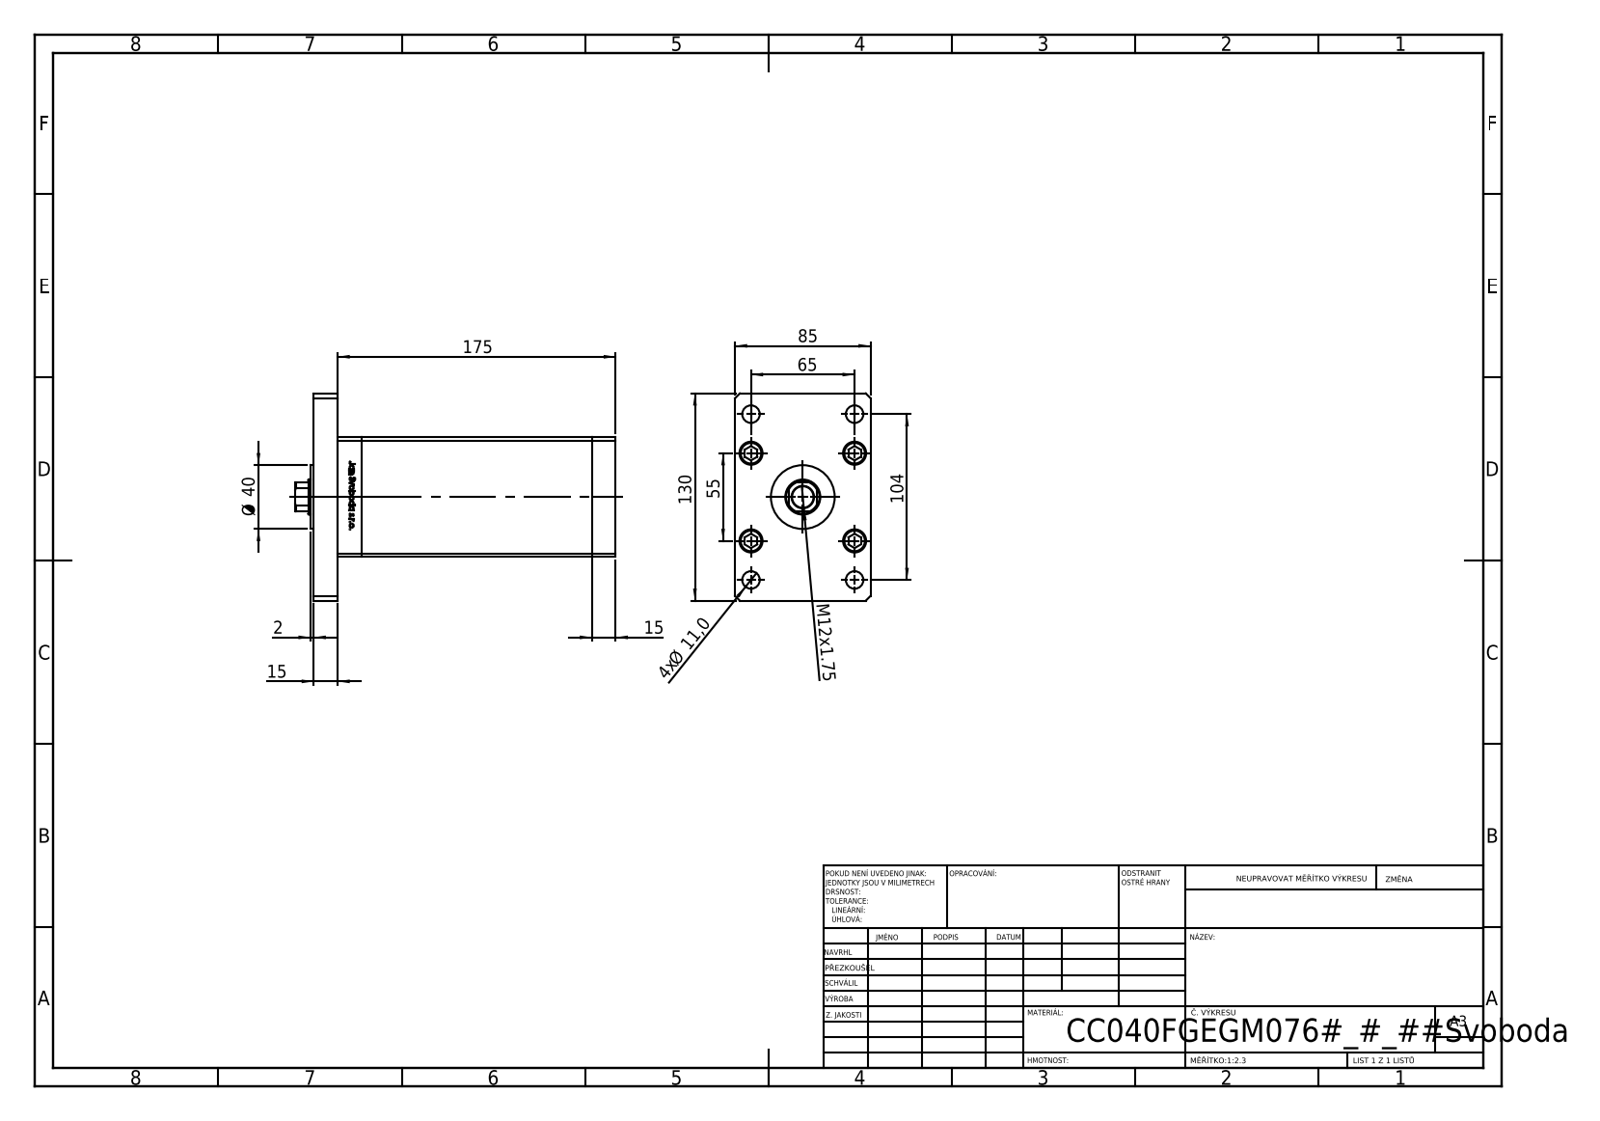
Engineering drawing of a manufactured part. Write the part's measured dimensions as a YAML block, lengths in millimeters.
part_name: "V220C_F; V220C_FRONT_F; V220C BACK_F; V220C_F_MIDDLE (+2 more)"
step_written_by: "SolidWorks 2019 (CONFIG_CONTROL_DESIGN)"
units: millimeters
bodies: {solids: 19, faces: 1310, planar: 517, cylindrical: 187, other: 606}
overall_size: [201, 130, 85]
volume: 1144000
surface_area: 196751
round_holes:
  - {diameter: 11, count: 9}
  - {diameter: 15.5, count: 5}
  - {diameter: 10, count: 4}
  - {diameter: 14.5, count: 4}
  - {diameter: 2, count: 2}
  - {diameter: 13.16, count: 2}
  - {diameter: 13.5, count: 1}
  - {diameter: 22, count: 1}
  - {diameter: 23.5, count: 1}
round_bosses_or_shafts:
  - {diameter: 8, count: 9}
  - {diameter: 14.5, count: 5}
  - {diameter: 40, count: 1}
partial_cylinders:
  - {radius: 0.93, count: 2}
  - {radius: 10.5, count: 1}
face_to_face_distances: [15, 85, 159.5, 174.5, 75, 30, 144.5, 189.5, 10.5, 27.5]
hole_center_spacings: [28, 24.5, 42.57, 61.32, 65, 69.46, 79.5, 102.69]
